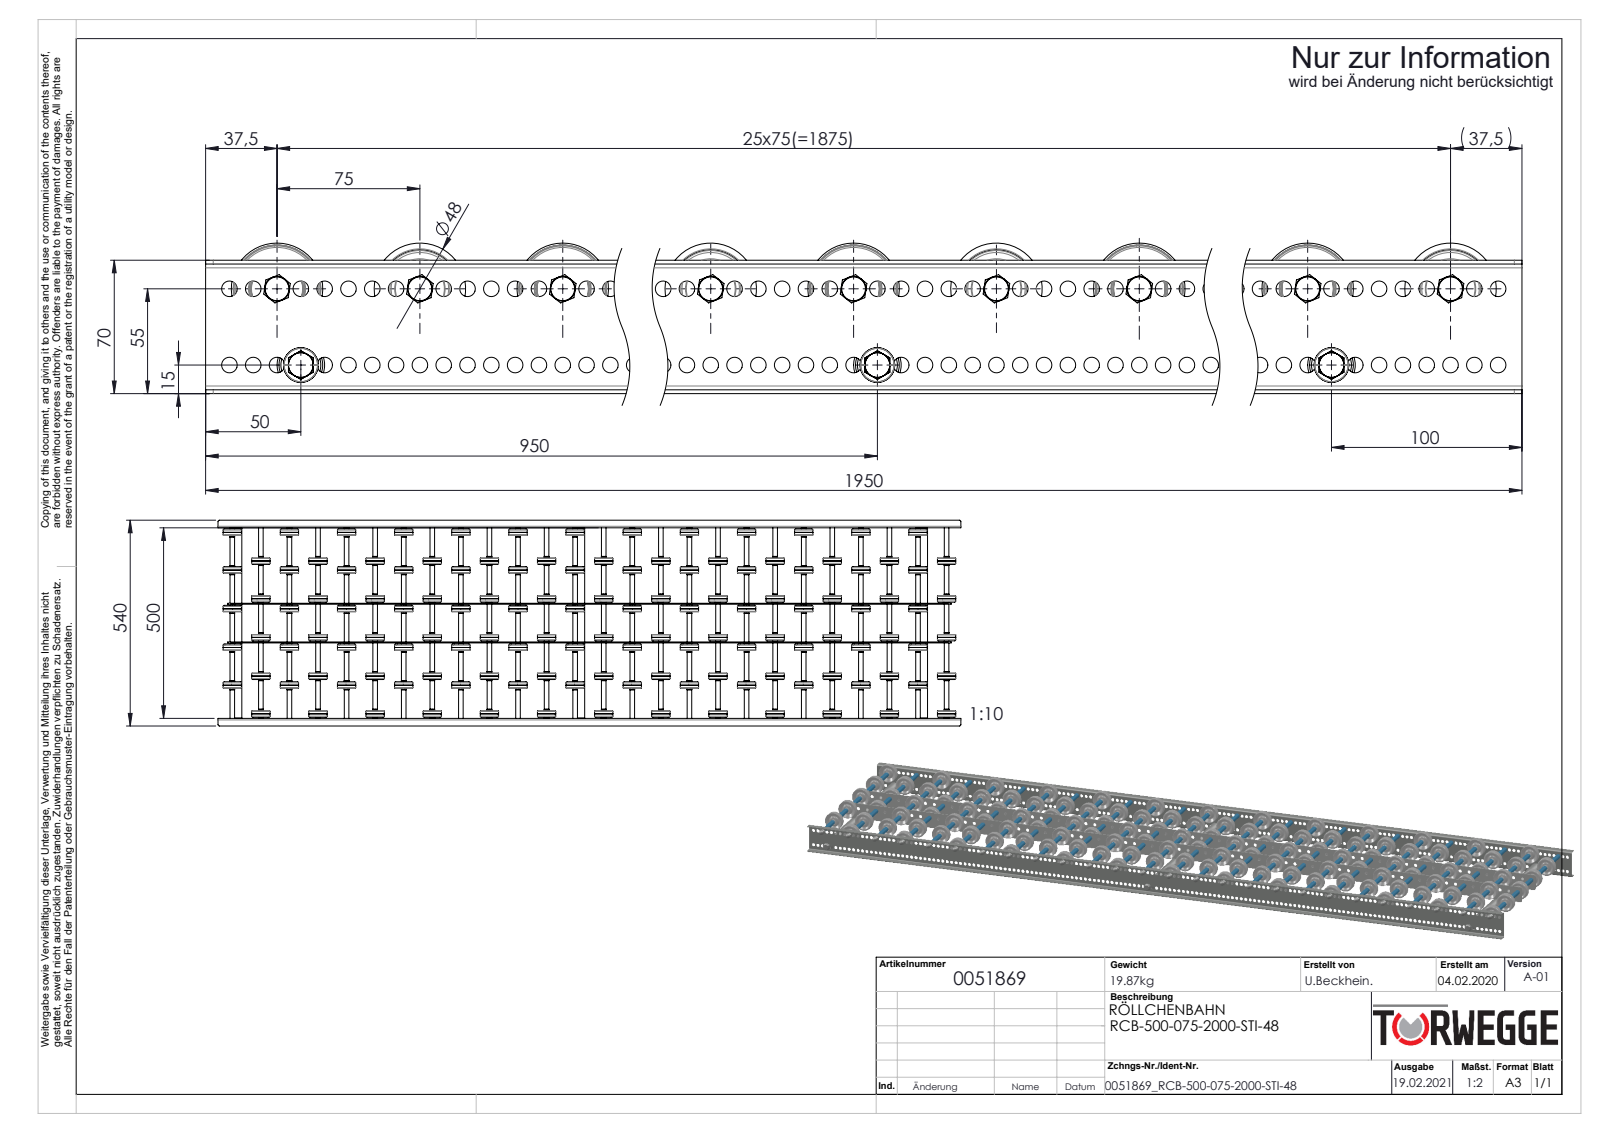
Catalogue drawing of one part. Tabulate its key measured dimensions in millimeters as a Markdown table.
| quantity | value |
| --- | --- |
| part name | K0011528_2200-48-8; Hutmutter_DIN_1587_M8; S100994_Sperrzahnschraube_M08x16-8.8-A2K; S106837_Gewindestange-M8-KFG_L520 (+6 more) |
| STEP written by | SolidWorks 2020 (AUTOMOTIVE_DESIGN) |
| units | millimeters |
| bodies | 487 solids, 14802 faces (2982 planar, 5788 cylindrical, 6032 other) |
| overall size | 1950 × 540 × 79 |
| volume | 5 226 000 mm³ |
| surface area | 4 013 000 mm² |
| round holes (diameter × count) | 8.2 × 310, 8.5 × 76, 6.65 × 26, 8 × 26, 9.65 × 26, 15 × 26, 41 × 26, 6.8 × 3, 21 × 3 |
| round bosses / shafts (diameter × count) | 48 × 26, 13 × 26, 12.5 × 26, 12.4 × 26, 12 × 26, 11.5 × 26, 25 × 3, 8 × 3 |
| partial cylindrical surfaces (radius × count) | 4 × 8, 2 × 4, 5 × 4 |
| main face-to-face distances | 2, 101.5, 200.5, 302, 87, 12, 99, 75, 502, 111 |
| hole center spacings | 12.5, 25, 37.5, 50, 62.5, 75, 87.5, 100 |
